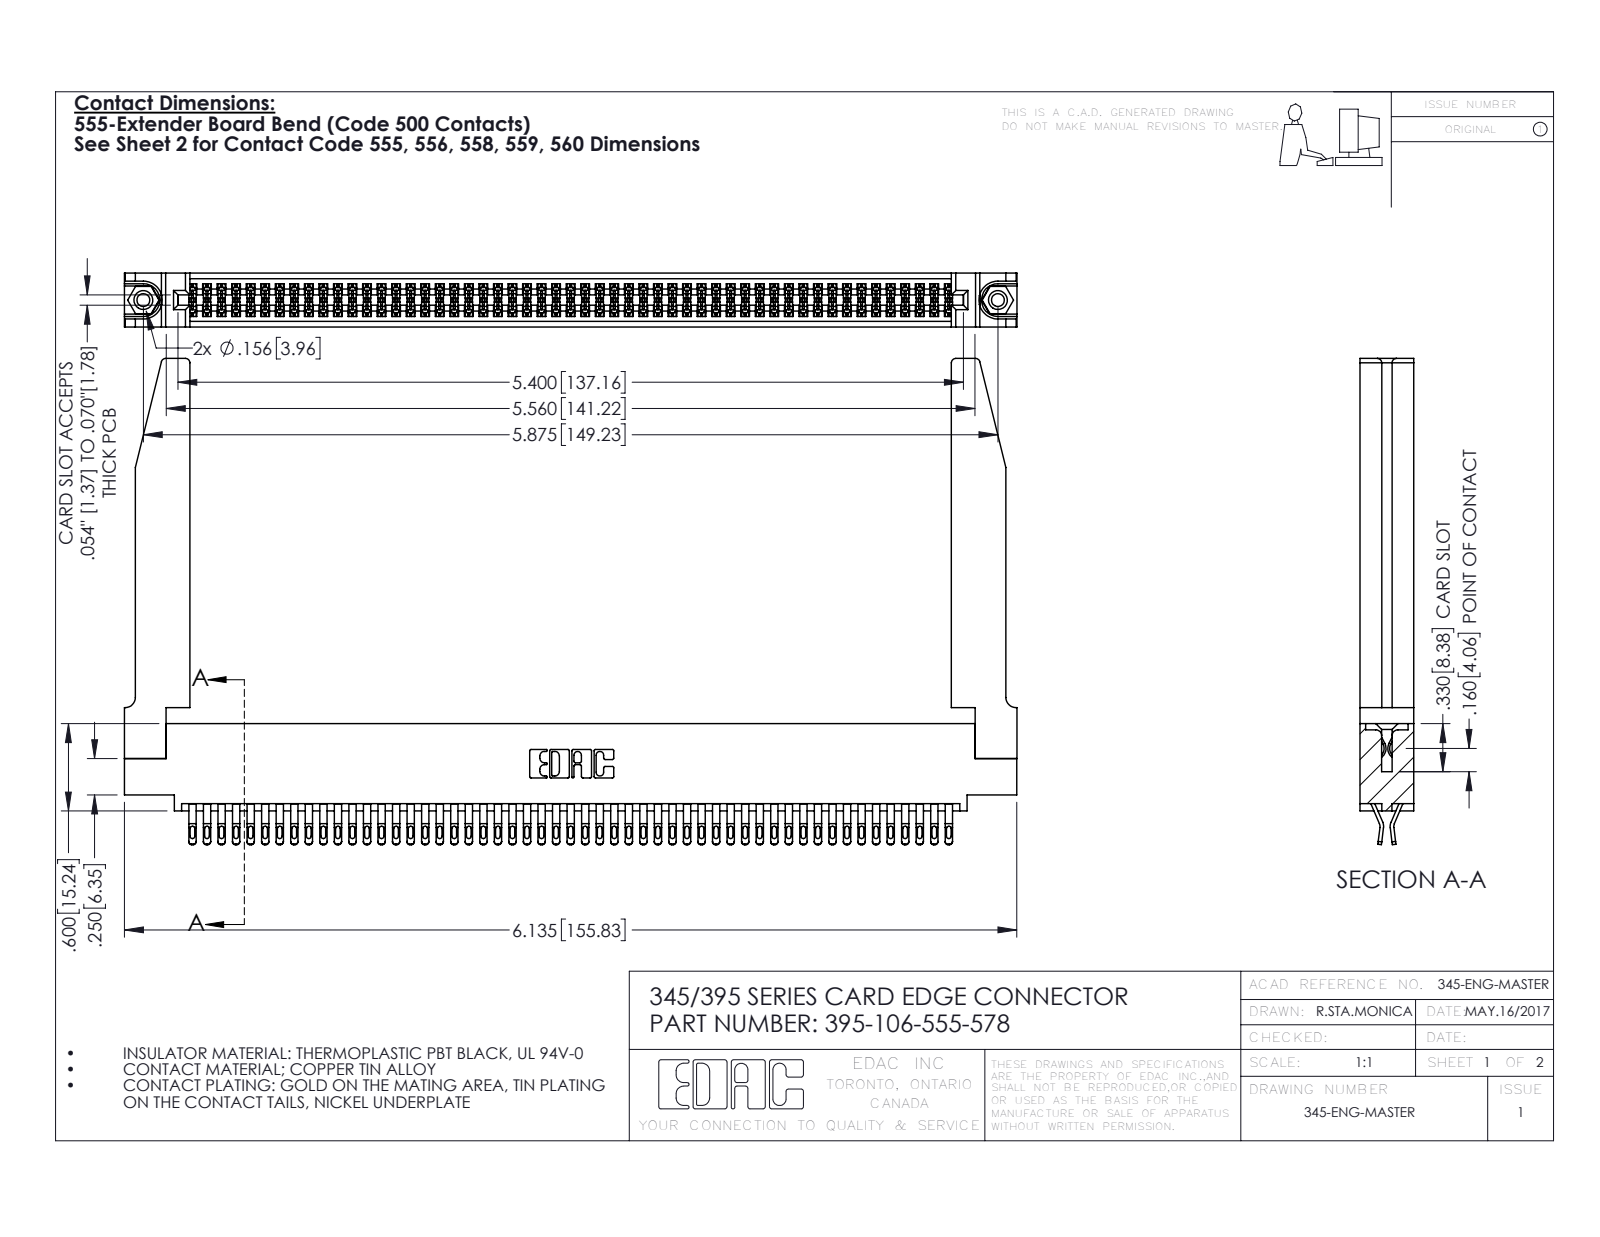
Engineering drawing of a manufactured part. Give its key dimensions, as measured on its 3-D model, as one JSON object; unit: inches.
{"part_name": "345-220-078_345-220-078; 345-250-001_345-250-001-102; 345-292-001_555 Tail; 345 Part_0.110 Offset - 0.156 Dia-TH (+1 more)", "step_written_by": "SolidWorks 2016 (CONFIG_CONTROL_DESIGN)", "units": "inches", "bodies": {"solids": 111, "faces": 6300, "planar": 3512, "cylindrical": 2736, "other": 52}, "overall_size": [6.136, 3.342, 0.37], "volume_in3": 1.419, "surface_area_in2": 48.19, "round_holes": [[0.089, 2], [0.125, 2], [0.156, 2], [0.064, 1]], "round_bosses_or_shafts": [[0.155, 2]], "partial_cylinders_radius": [[0.016, 265], [0.02, 212], [0.006, 159], [0.01, 22], [0.03, 8], [0.007, 6], [0.031, 6], [0.026, 3]], "face_to_face_distances": [0.072, 0.37, 0.298, 0.025, 0.2, 0.098, 0.272, 0.225, 0.175, 0.148], "hole_center_spacings": [0.27, 5.639, 5.875]}
